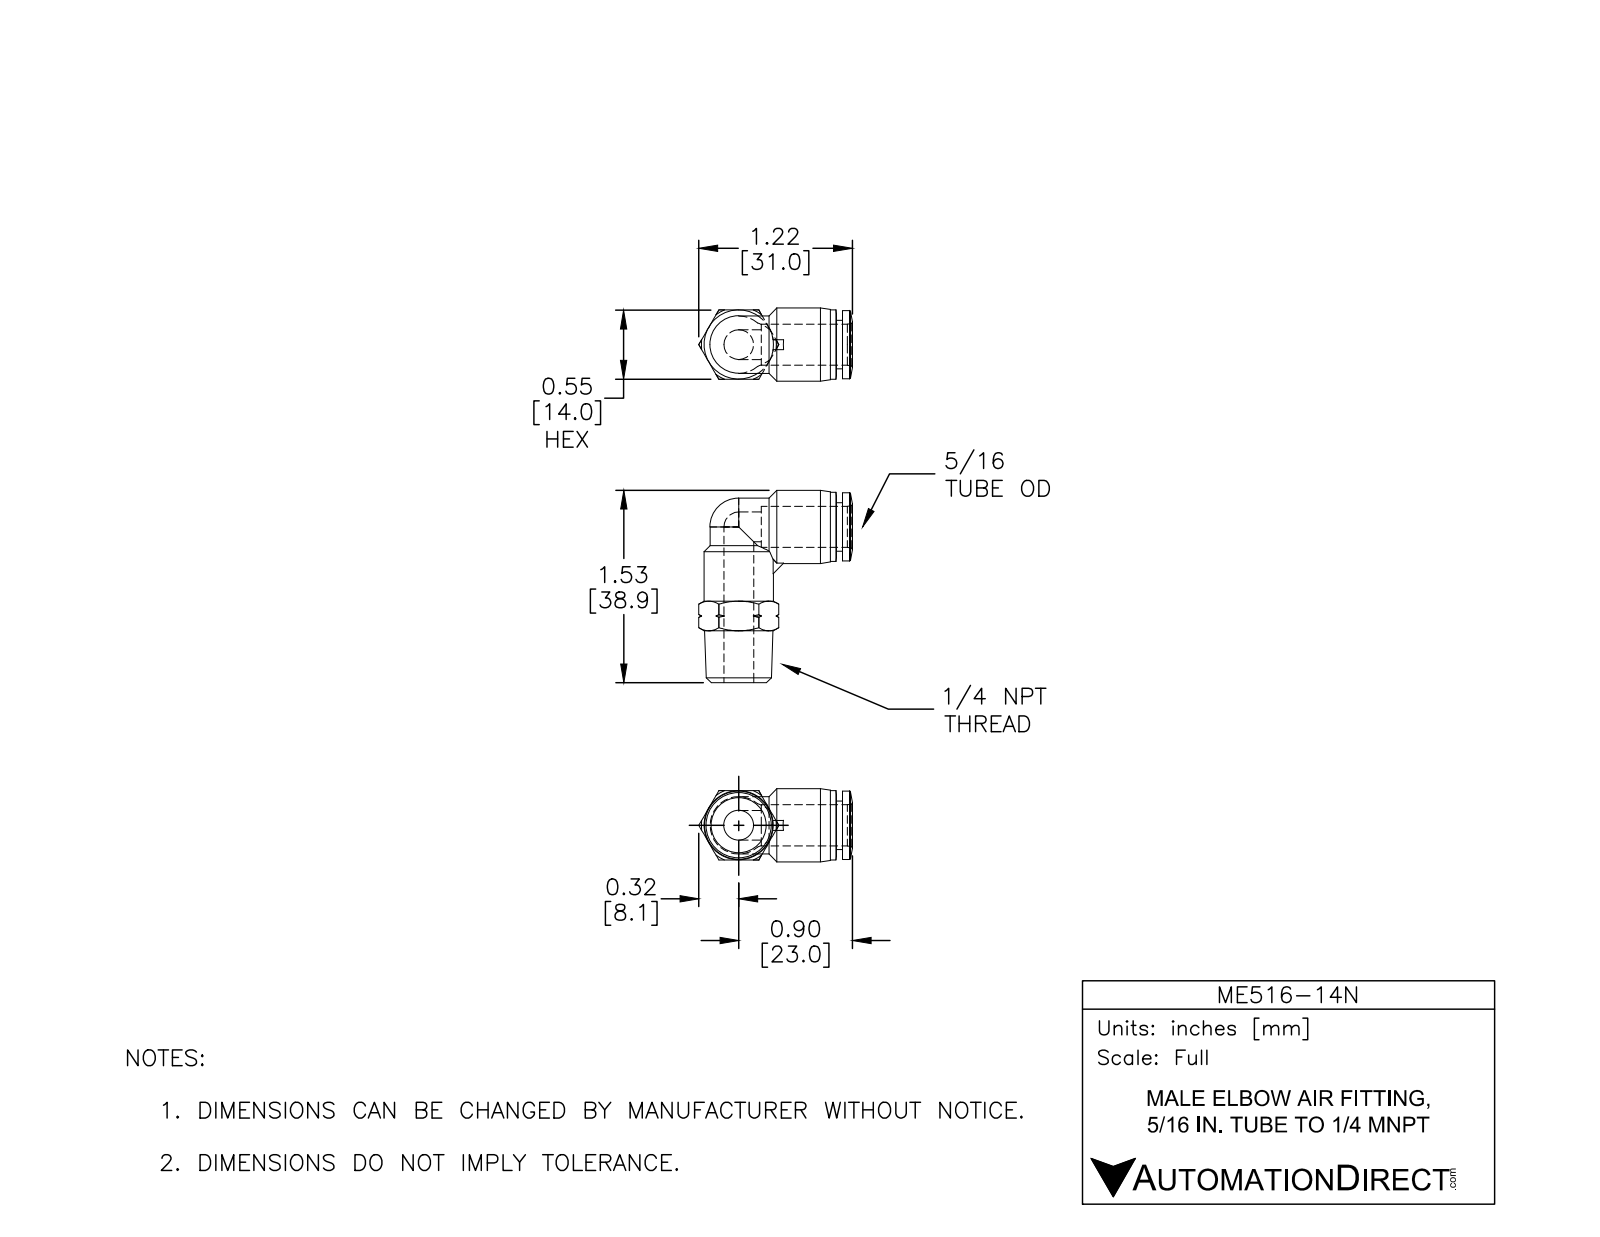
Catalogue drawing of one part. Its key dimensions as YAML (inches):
part_name: "ME516-14N"
step_written_by: "SolidWorks 2015 (CONFIG_CONTROL_DESIGN)"
units: inches
bodies: {solids: 1, faces: 88, planar: 15, cylindrical: 21, other: 52}
overall_size: [1.531, 1.222, 0.583]
volume: 0.353
surface_area: 5.944
round_holes:
  - {diameter: 0.236, count: 2}
  - {diameter: 0.327, count: 1}
round_bosses_or_shafts:
  - {diameter: 0.551, count: 2}
  - {diameter: 0.583, count: 1}
  - {diameter: 0.543, count: 1}
  - {diameter: 0.457, count: 1}
  - {diameter: 0.386, count: 1}
partial_cylinders:
  - {radius: 0.228, count: 1}
face_to_face_distances: [0.551, 0.047, 0.598, 0.646, 0.236, 0.315, 0.549, 0.049, 0.096, 0.413]
